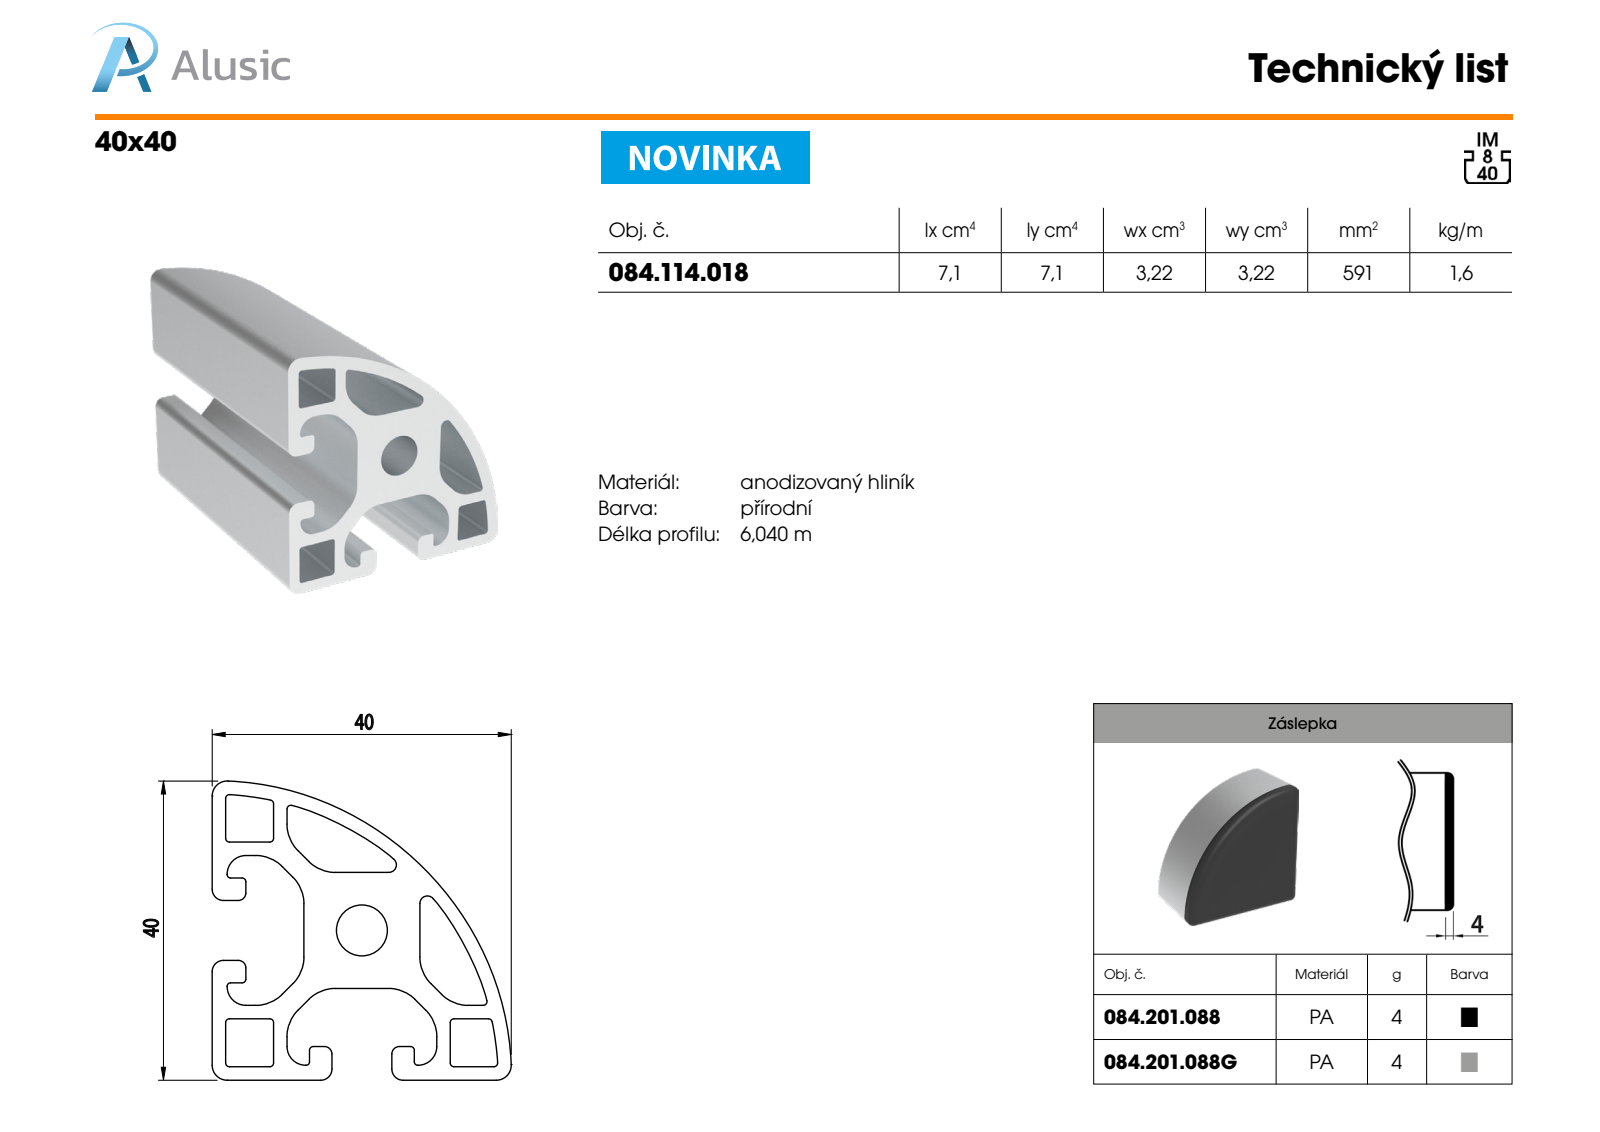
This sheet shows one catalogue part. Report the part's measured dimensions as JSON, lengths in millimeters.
{"part_name": "084.114.018", "step_written_by": "SolidWorks 2018 (AUTOMOTIVE_DESIGN)", "units": "millimeters", "bodies": {"solids": 1, "faces": 110, "planar": 48, "cylindrical": 62, "other": 0}, "overall_size": [100, 39.95, 39.95], "volume_mm3": 59075, "surface_area_mm2": 41399, "round_holes": [[6.8, 1]], "partial_cylinders_radius": [[0.5, 18], [5, 12], [1, 6], [0.45, 4], [1.5, 4], [2.5, 4], [2, 3], [38, 1]], "face_to_face_distances": [1.8, 8.2, 4.05, 19.55, 6.4, 3, 12.25, 10.45, 27.75, 25.95]}
